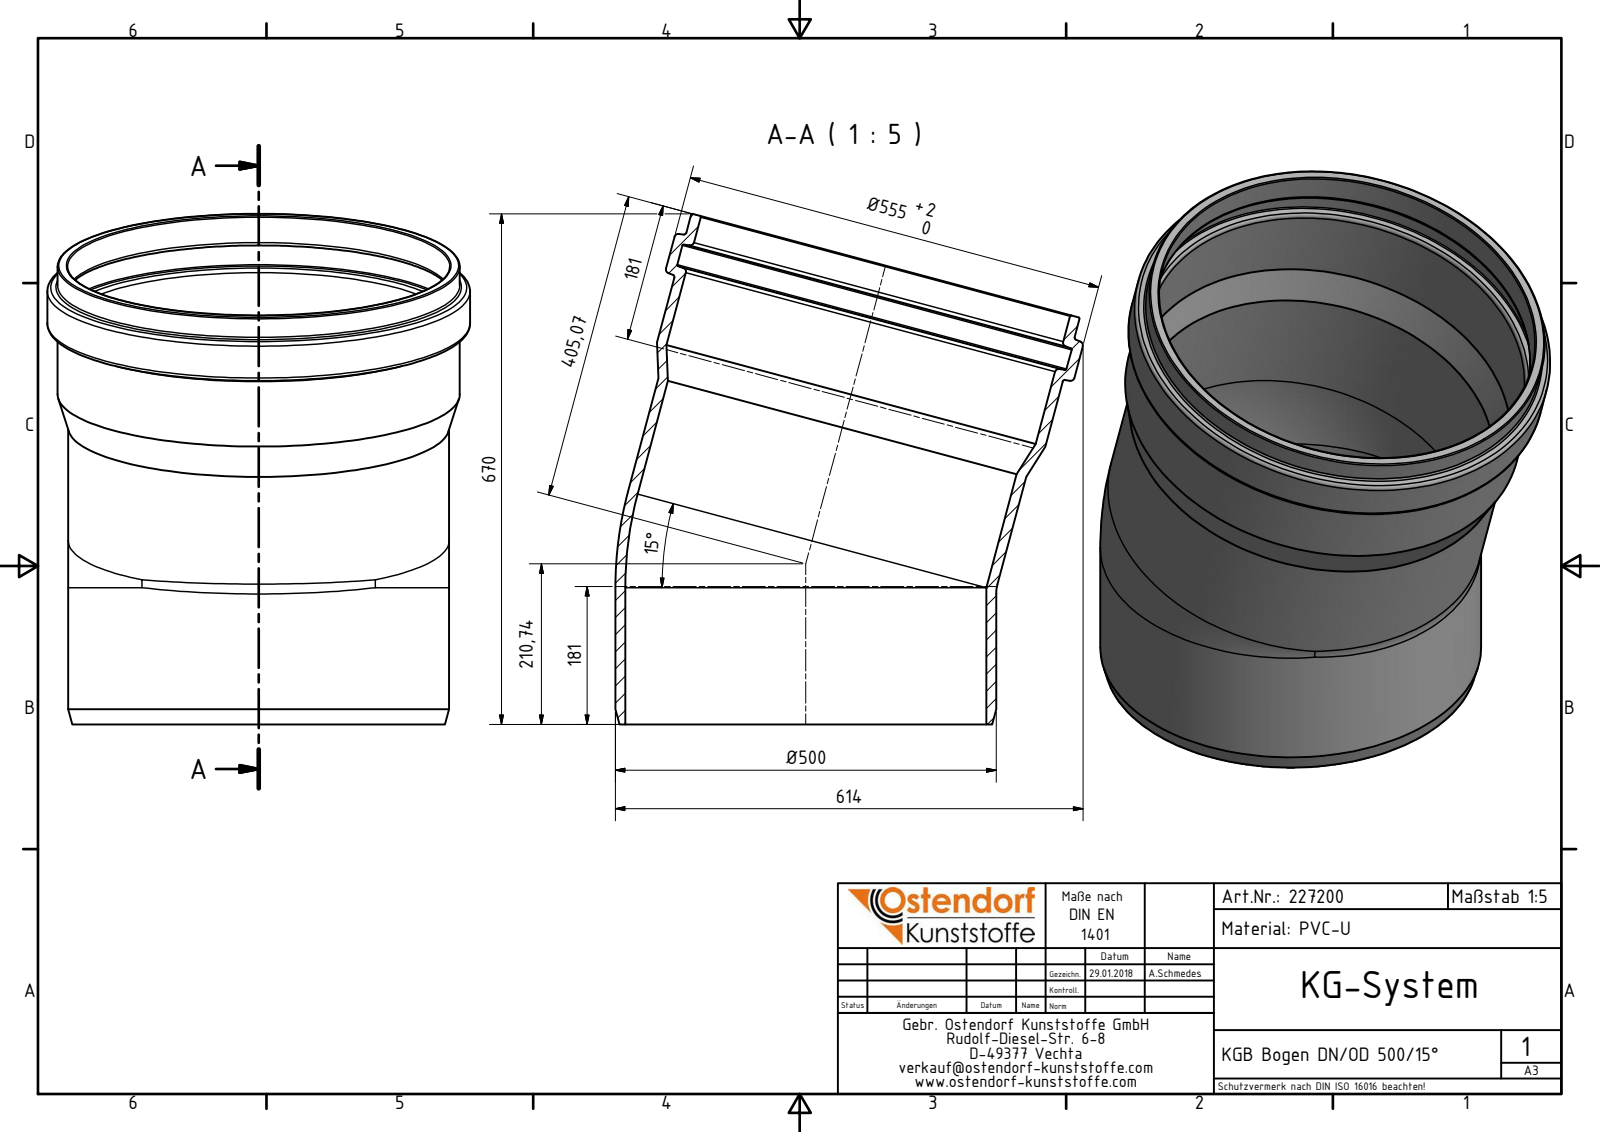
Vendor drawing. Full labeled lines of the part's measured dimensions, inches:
Part name (STEP PRODUCT): 227200 KGB Bogen DN_OD 500_15°
STEP written by: Autodesk Inventor 2016 (AUTOMOTIVE_DESIGN)
Units: inches
Bodies: 1 solid, 32 faces (2 planar, 10 cylindrical, 20 other)
Overall size (bounding box): 26.378 × 24.173 × 21.85
Volume: 767.7 in³ · Surface area: 3 143 in²
Round holes (diameter × count): ⌀18.661 ×2, ⌀19.764 ×2, ⌀20.827 ×1
Round bosses / shafts (diameter × count): ⌀20.787 ×2, ⌀19.685 ×2, ⌀21.85 ×1
